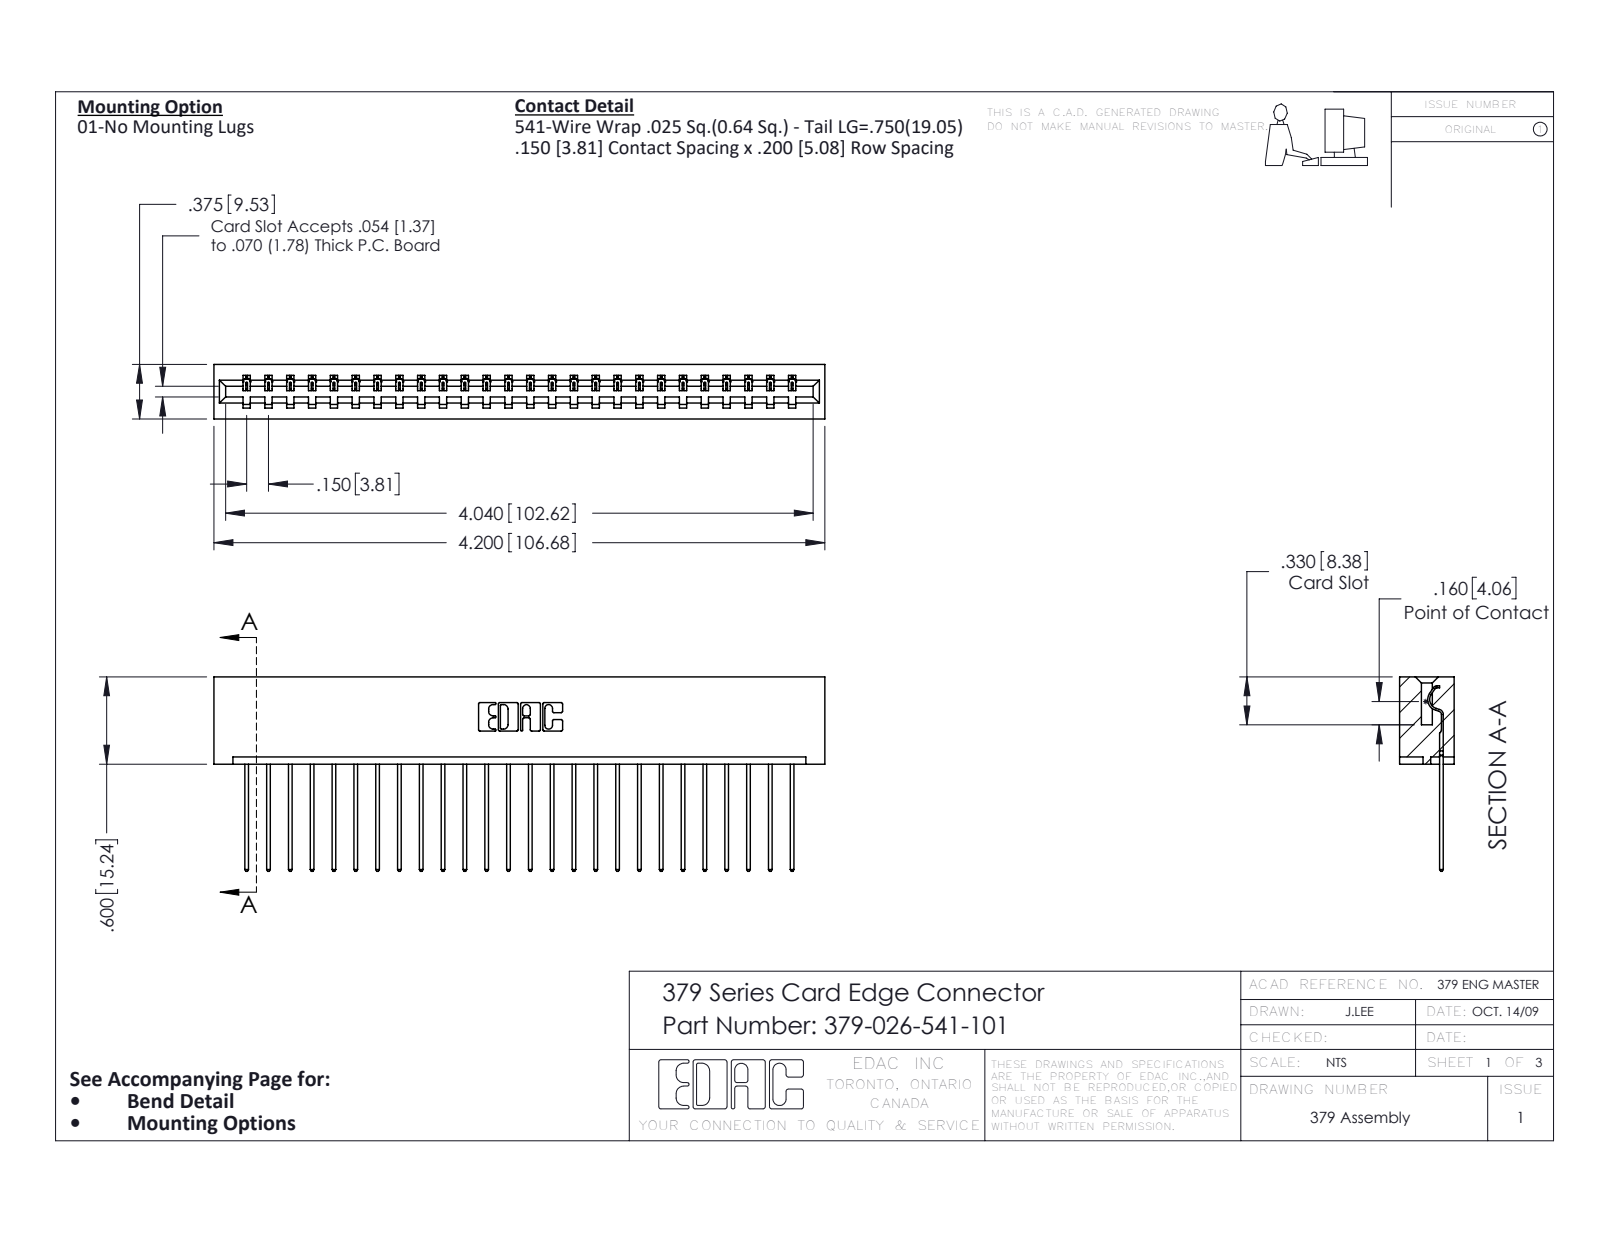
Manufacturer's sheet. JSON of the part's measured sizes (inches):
{"part_name": "379 Part_Lugless; 345-292-001_345-293-141; 379-026-541-101", "step_written_by": "SolidWorks 2016 (CONFIG_CONTROL_DESIGN)", "units": "inches", "bodies": {"solids": 27, "faces": 1614, "planar": 1158, "cylindrical": 456, "other": 0}, "overall_size": [4.2, 1.337, 0.375], "volume_in3": 0.721, "surface_area_in2": 19.39, "partial_cylinders_radius": [[0.006, 52], [0.01, 52], [0.01, 22], [0.007, 6], [0.031, 6], [0.026, 3], [0.014, 1], [0.022, 1]], "face_to_face_distances": [0.3, 0.075, 0.375, 0.225, 0.1, 0.275, 0.025, 0.6, 0.15, 0.45]}
